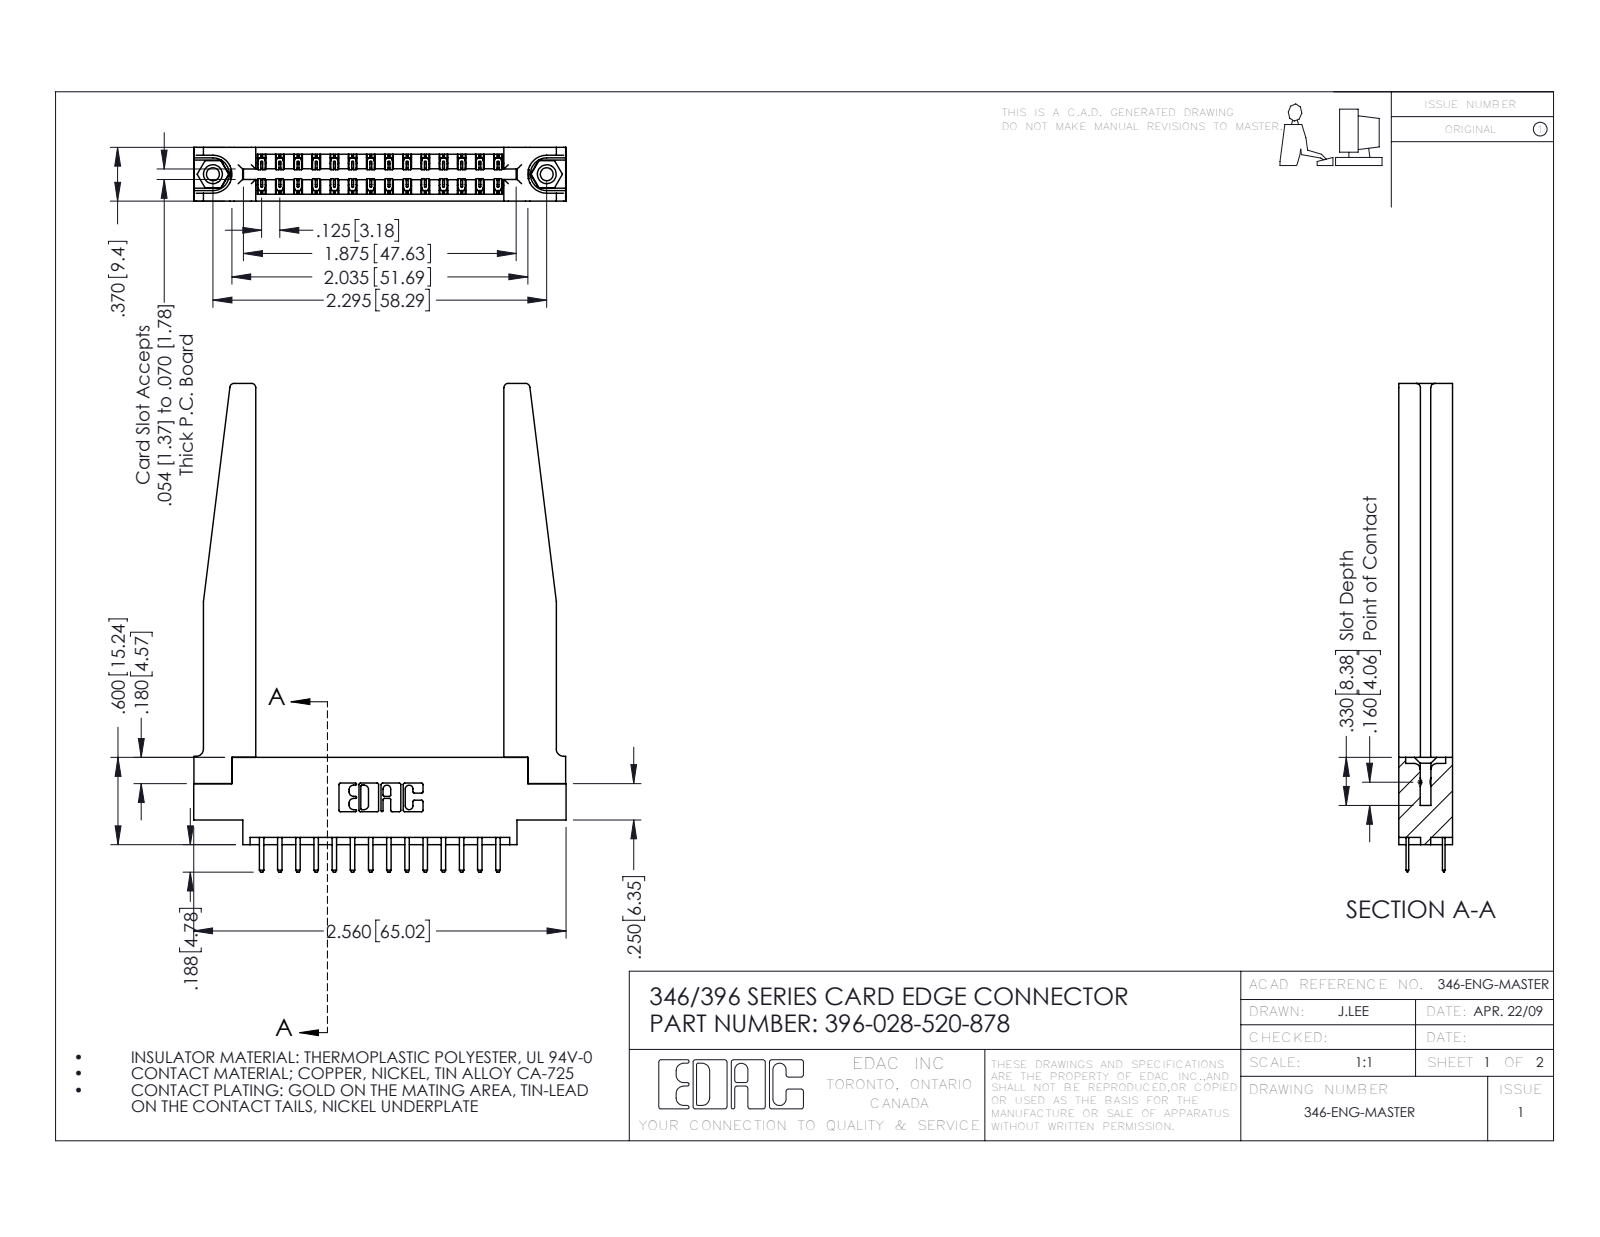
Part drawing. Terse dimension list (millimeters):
name: 345-292-001_345-293-120; 396-028-520-878; 345-250-001_345-250-001-102; 346 Part_0.170 Offset - 0.156 Dia-TH (+1 more)
written by: SolidWorks 2016 (CONFIG_CONTROL_DESIGN)
unit: mm
bodies: 33 solids, 1928 faces (1258 planar, 618 cylindrical, 52 other)
size: 85.3 × 65 × 9.4
volume: 12 900 mm³; area: 14 440 mm²
holes: 2× ⌀2.3, 2× ⌀3.2, 2× ⌀4, 1× ⌀1.6
bosses: 2× ⌀3.9
rounds: 42× R0.2, 32× R0.3, 22× R0.3, 8× R0.8, 6× R0.2, 6× R0.8, 3× R0.7, 2× R0.4
face distances: 9.4, 3.8, 1.8, 3.8, 1.2, 8.2, 6.4, 2.6, 5.6, 4.4
hole spacings: 6.2, 53.1, 58.3
